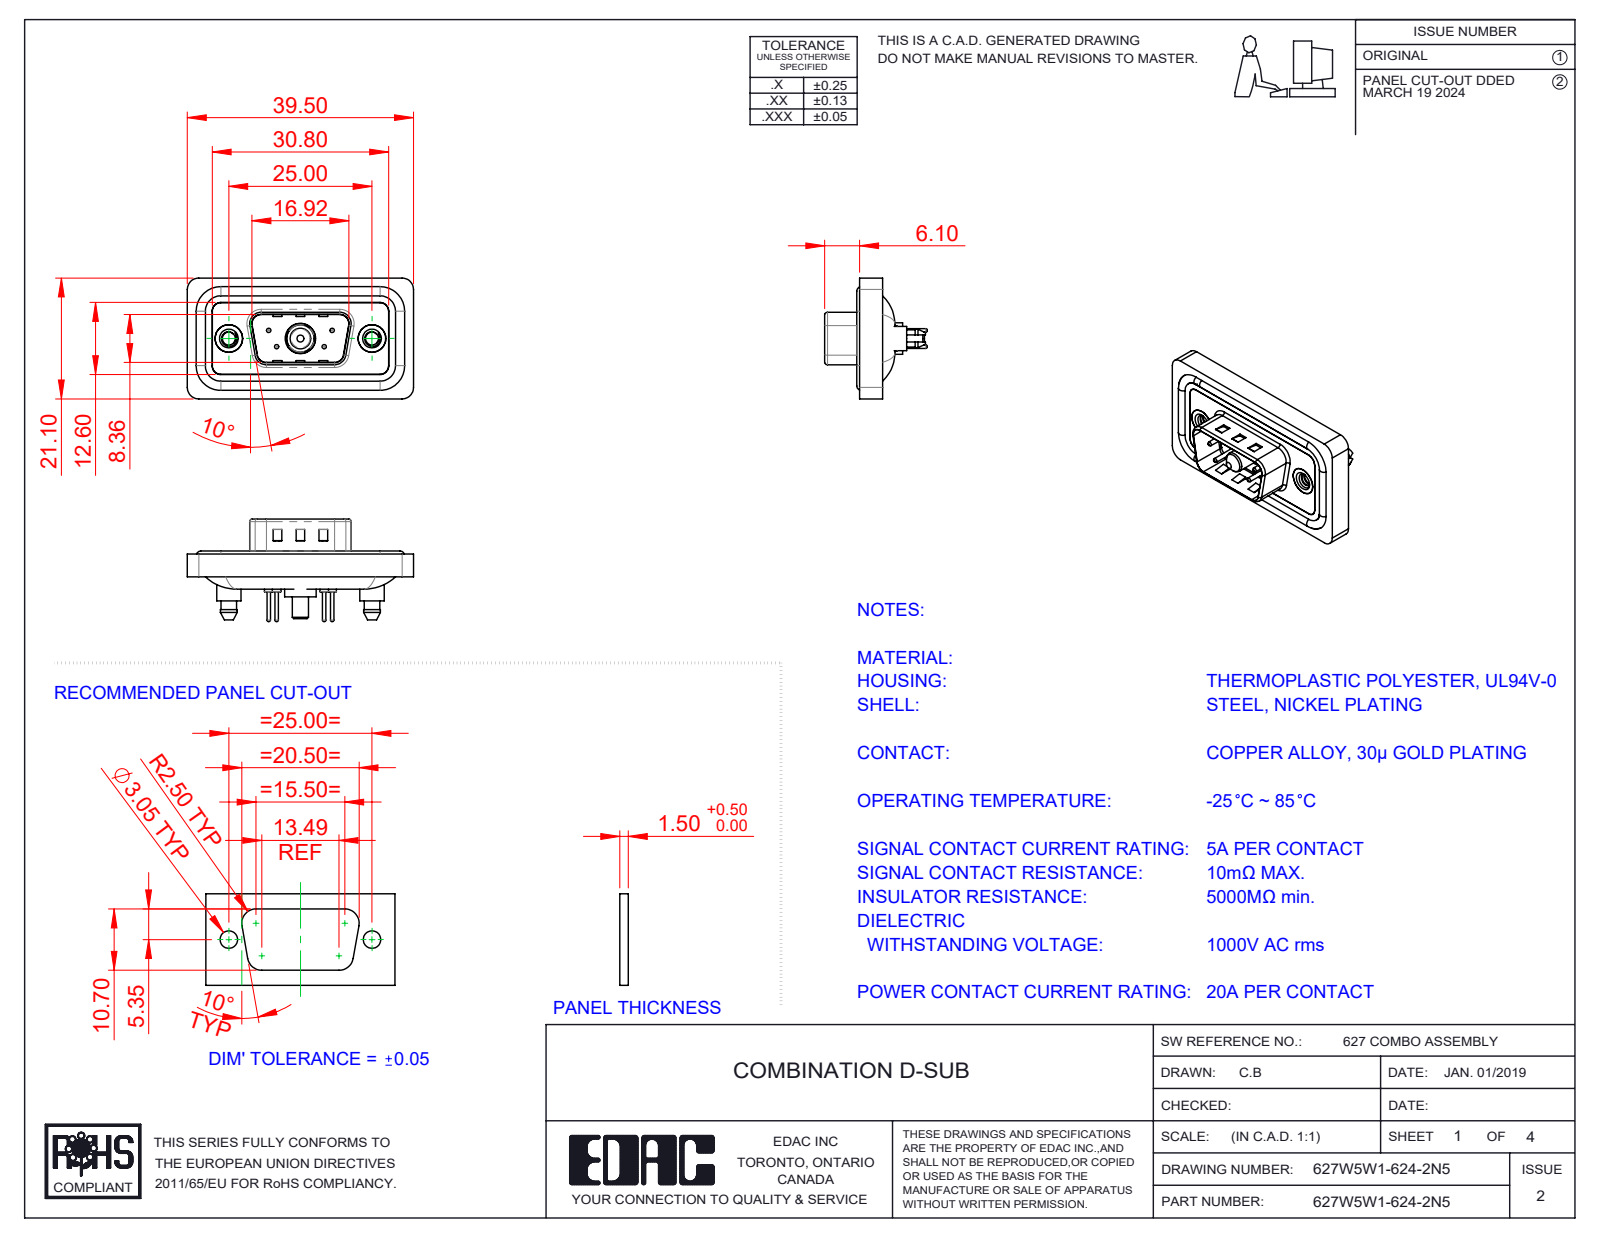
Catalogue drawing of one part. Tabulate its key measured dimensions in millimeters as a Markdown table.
| quantity | value |
| --- | --- |
| part name | Power Pin_20A S; 627Combo Contact Row 1_24; 627Combo Shell Rear_09 Contacts; 627Combo Waterproof Housing_09 Contacts (+5 more) |
| STEP written by | SolidWorks 2023 (CONFIG_CONTROL_DESIGN) |
| units | millimeters |
| bodies | 13 solids, 648 faces (199 planar, 287 cylindrical, 162 other) |
| overall size | 39.5 × 21.1 × 17.9 |
| volume | 4 521 mm³ |
| surface area | 7 274 mm² |
| round holes (diameter × count) | 0.75 × 4, 1.6 × 4, 2 × 4, 2.26 × 2, 4 × 2, 4.8 × 2, 5 × 2, 4.85 × 1, 5.3 × 1 |
| round bosses / shafts (diameter × count) | 1.6 × 4, 1.5 × 4, 0.6 × 4, 5.4 × 2, 4.9 × 2, 4.25 × 2, 5.5 × 1, 5.2 × 1 |
| partial cylindrical surfaces (radius × count) | 1.5 × 24, 2 × 18, 1.6 × 10, 0.5 × 8, 0.25 × 4, 0.6 × 4, 0.65 × 4, 0.9 × 4 |
| main face-to-face distances | 0.4, 1.1, 2.9, 1.6, 1.5, 3.1, 0.5, 2.5, 4, 0.8 |
| hole center spacings | 3.16, 5.72, 7.1, 12.5, 18.1, 4.39, 4.4, 8.31 |
